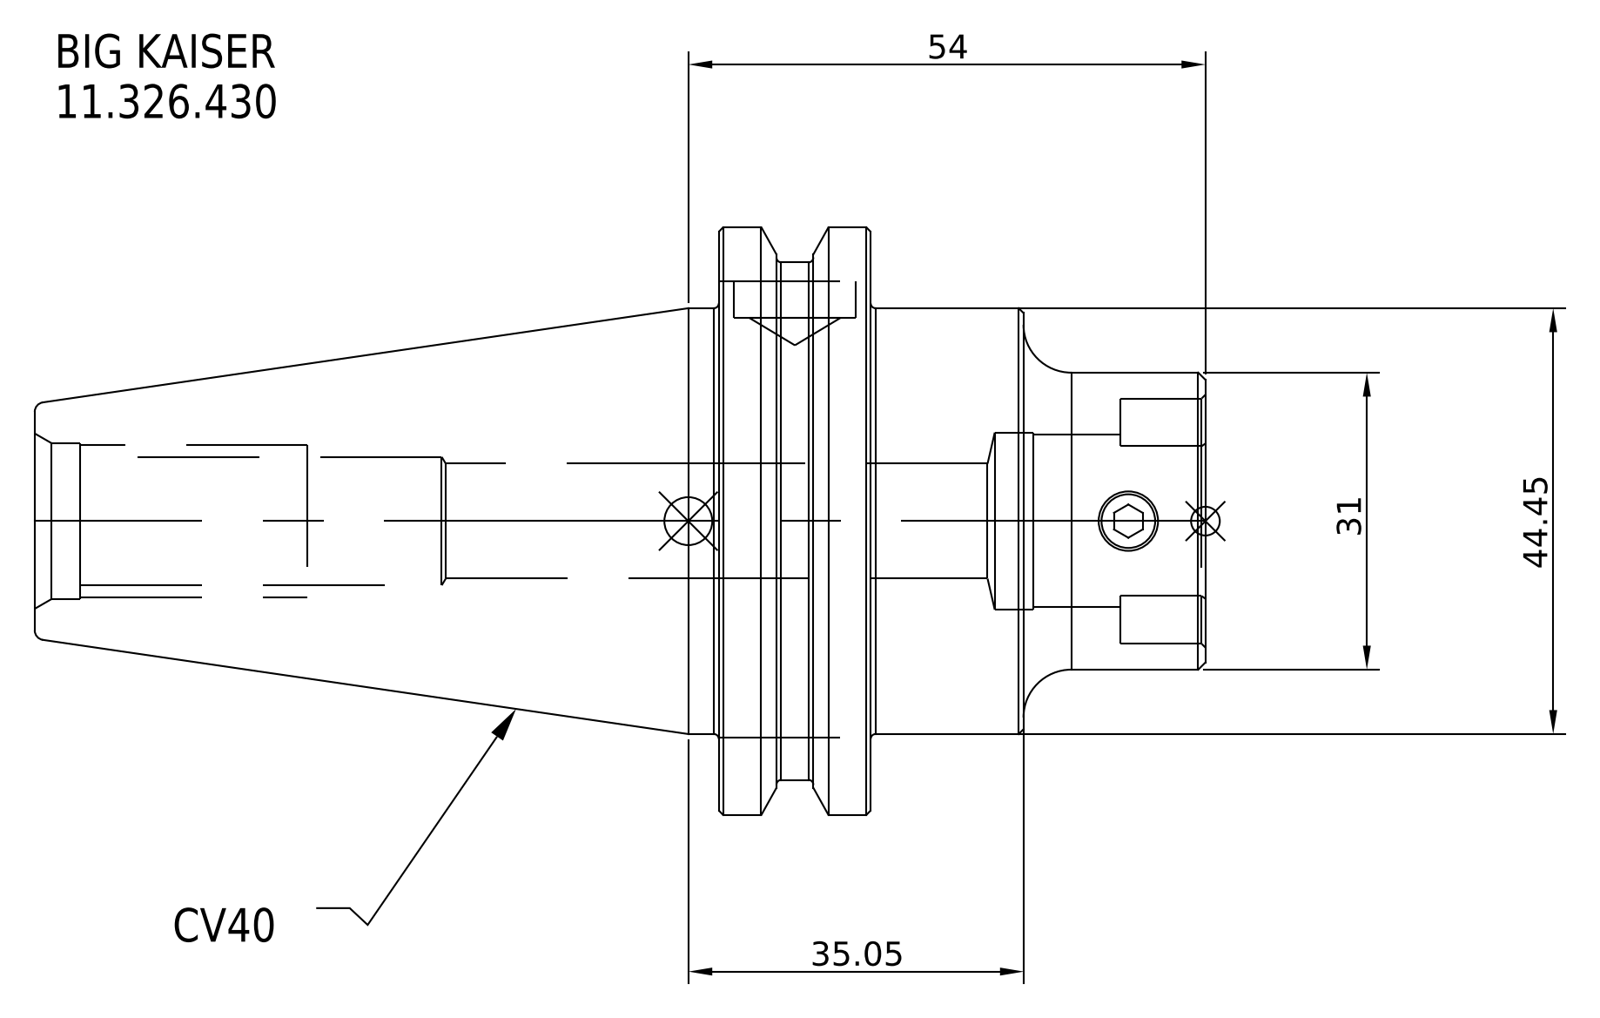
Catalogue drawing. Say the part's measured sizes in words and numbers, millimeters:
The part is named "11_326_430". Its 3-D file was written by "SolidWorks 2021 (CONFIG_CONTROL_DESIGN)". It is 1 solid with 27 faces: 7 planar, 12 cylindrical and 8 other. Overall it measures 122.25 by 63.5 by 63.5 millimeters. Its volume is 157 007 cubic millimeters and its surface area 21 005 square millimeters. Round bosses or shafts: 1 of diameter 63.5, 1 of diameter 56.36, 1 of diameter 44.45, 1 of diameter 31. The main face-to-face distances are 15.88, 34.95, 50.83, 122.25, 87.3, 71.42, 18.95, 16, 31.88, 103.3.
